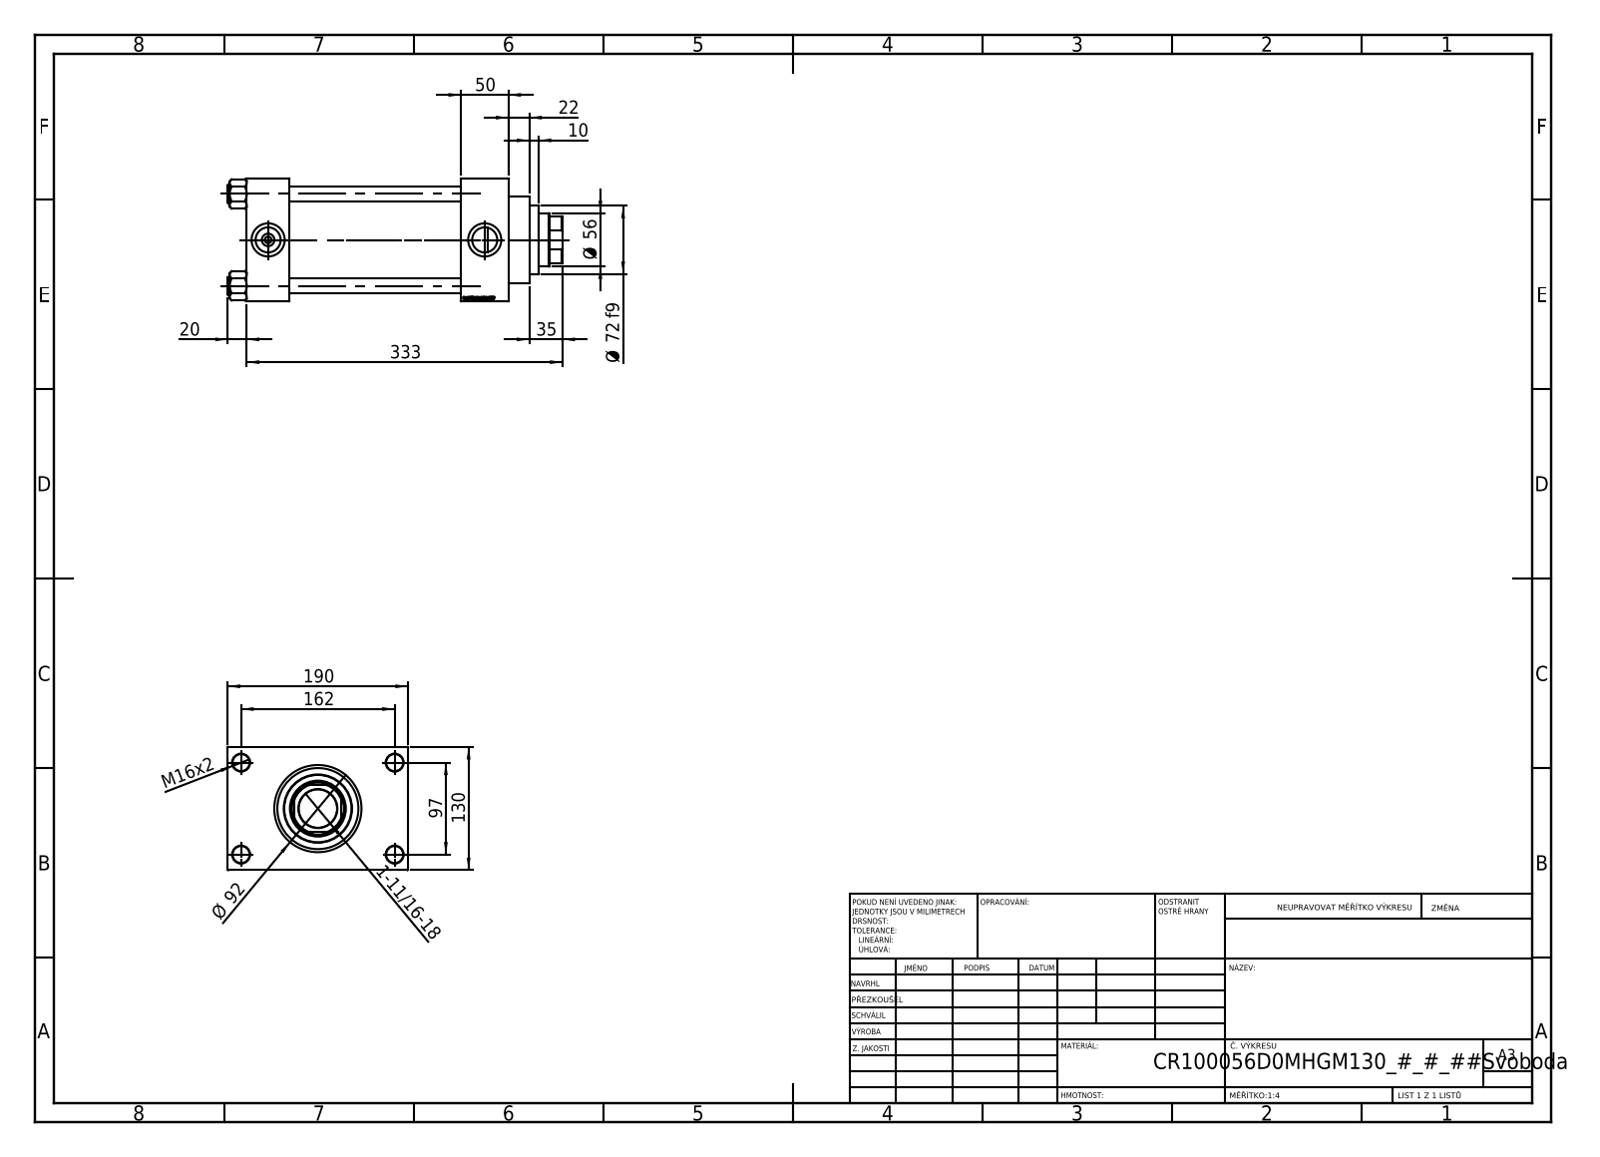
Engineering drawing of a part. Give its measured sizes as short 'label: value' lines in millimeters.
name: V215_VC_A; V215CR_D_Body; V215CR_D_TYCINKA; V215CR_VCP_D (+1 more)
written by: SolidWorks 2019 (CONFIG_CONTROL_DESIGN)
unit: mm
bodies: 11 solids, 1151 faces (545 planar, 88 cylindrical, 518 other)
size: 353 × 190 × 130
volume: 3 094 000 mm³; area: 475 021 mm²
holes: 4× ⌀16, 4× ⌀18, 2× ⌀7, 2× ⌀26.44, 2× ⌀35, 1× ⌀40.5, 1× ⌀56, 1× ⌀59, 1× ⌀76, 1× ⌀85.5, 1× ⌀100
bosses: 4× ⌀19, 1× ⌀106, 1× ⌀92, 1× ⌀72
rounds: 1× R27
face distances: 130, 50, 45, 226, 181, 276, 231, 30, 160, 190
hole spacings: 32.55, 68.52, 94.41, 96.9, 102.27, 129.45, 161.73, 97
